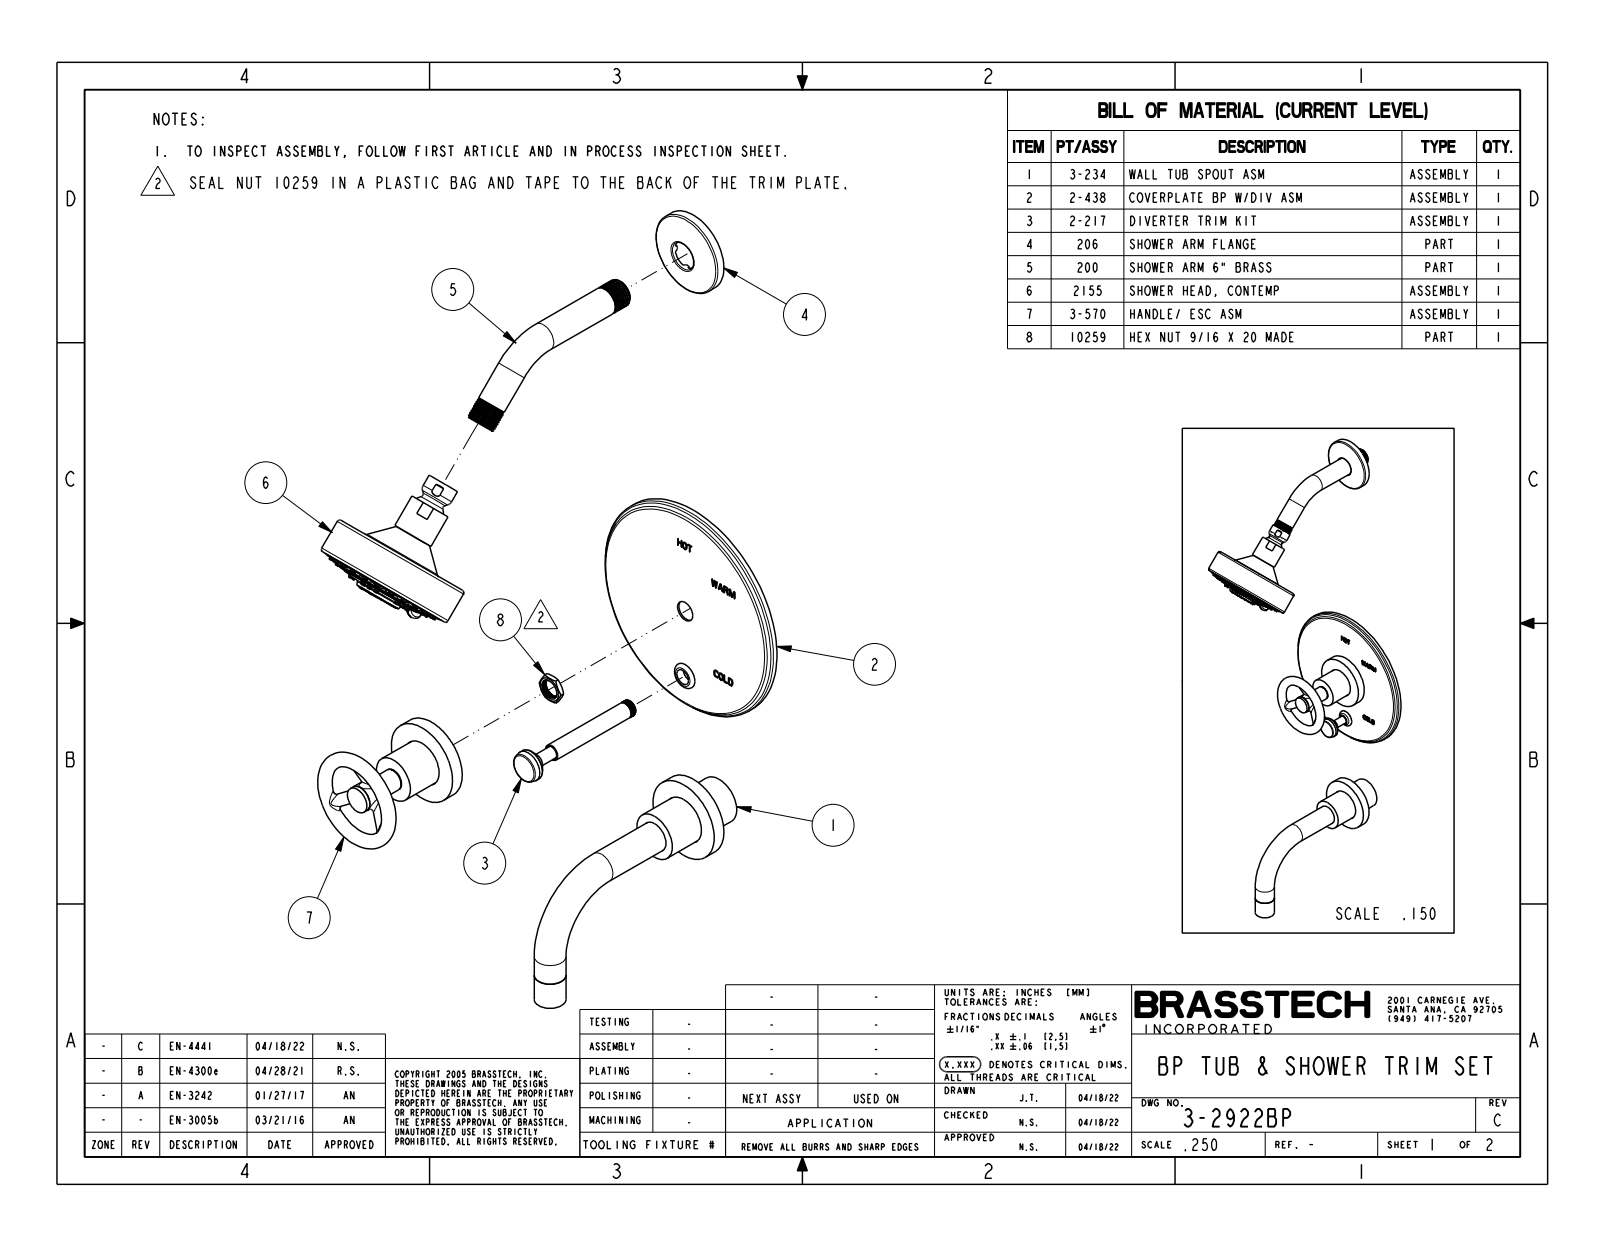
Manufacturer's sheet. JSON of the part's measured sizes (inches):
{"part_name": "3-2922BP", "step_written_by": "CREO PARAMETRIC BY PTC INC, 2018400 (CONFIG_CONTROL_DESIGN)", "units": "inches", "bodies": {"solids": 3, "faces": 1389, "planar": 404, "cylindrical": 222, "other": 763}, "overall_size": [23.63, 8.175, 6.5], "volume_in3": 44.75, "surface_area_in2": 209.4, "round_holes": [[0.059, 8], [0.925, 1]], "round_bosses_or_shafts": [[0.142, 39], [0.165, 23], [0.35, 3], [2.375, 2], [0.875, 2], [0.813, 2], [6.5, 1], [4, 1]], "partial_cylinders_radius": [[0.079, 8], [0.02, 2], [0.138, 1], [0.472, 1], [0.512, 1], [0.63, 1]], "face_to_face_distances": [0.313, 0.062, 0.688, 0.375, 0.375, 0.313, 1.796, 1.483, 1.421, 1.108], "hole_center_spacings": [0.443, 0.579, 0.818, 0.819, 1.069, 0.443, 0.578, 1.069]}
